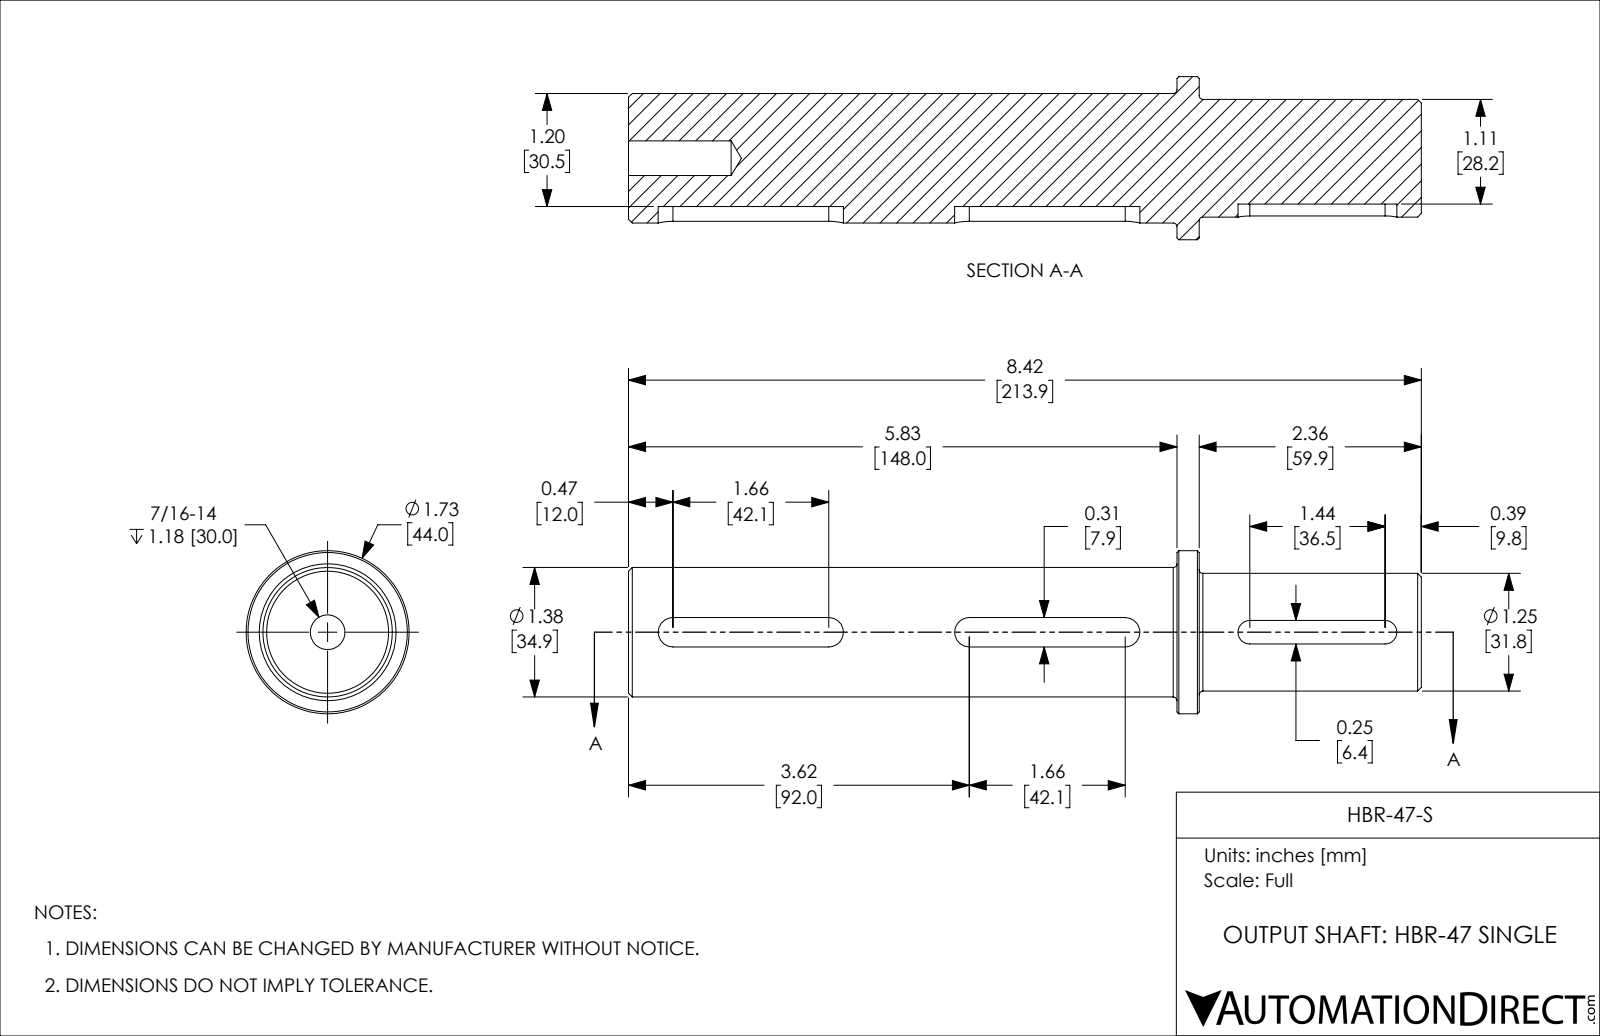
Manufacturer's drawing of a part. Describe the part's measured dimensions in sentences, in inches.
The part is named "HBR-47-S". Its 3-D file was written by "SolidWorks 2018 (AUTOMOTIVE_DESIGN)". It is 1 solid with 44 faces: 13 planar, 17 cylindrical and 14 other. Overall it measures 8.423 by 1.732 by 1.732 inches. Its volume is 11.72 cubic inches and its surface area 43.06 square inches. Round holes: 1 of diameter 0.368. Round bosses or shafts: 1 of diameter 1.732, 1 of diameter 1.375, 1 of diameter 1.25. Partial cylindrical surfaces (rounded edges, fillets, slot ends): 4 of radius 0.156, 2 of radius 0.125. The main face-to-face distances are 8.423, 6.063, 2.36, 5.827, 0.236, 2.596, 0.313, 0.027, 0.031, 0.281.
